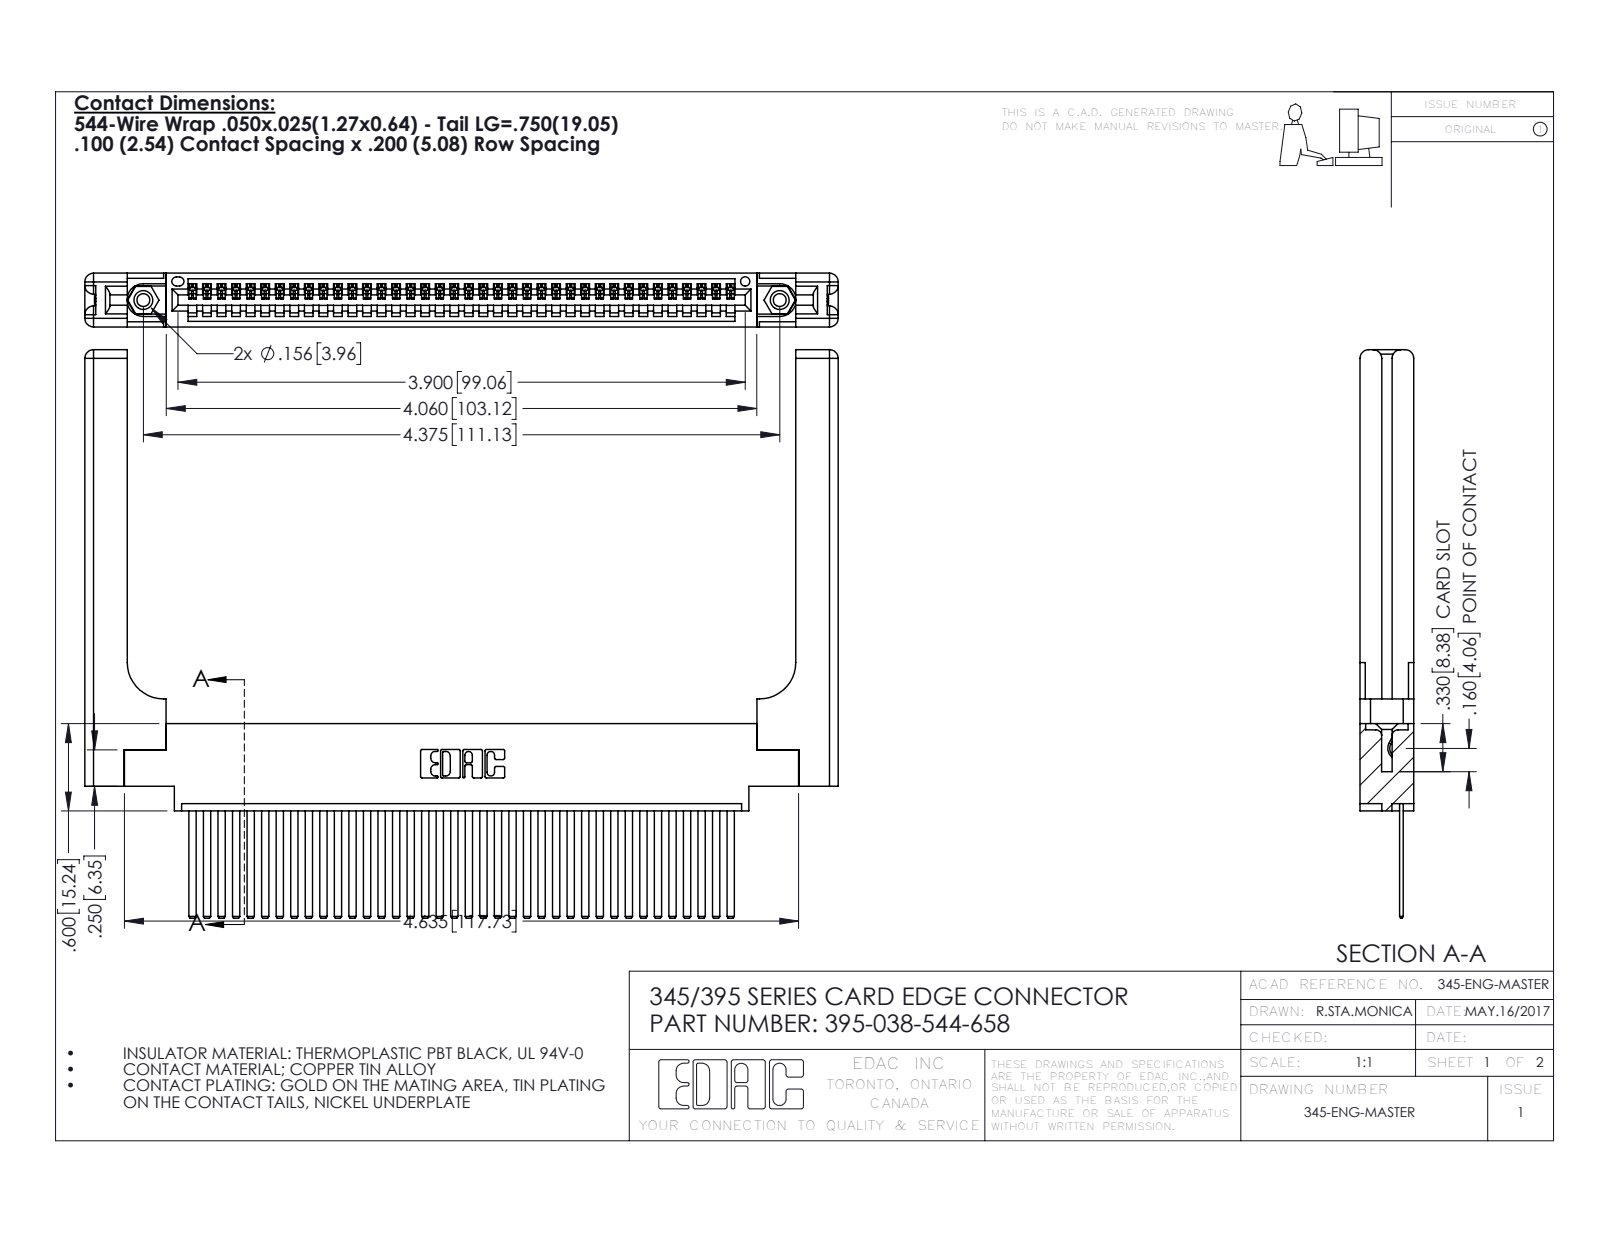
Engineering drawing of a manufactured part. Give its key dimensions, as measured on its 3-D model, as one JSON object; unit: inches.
{"part_name": "345 Part_0.170 Offset - 0.156 Dia-TH; 345-220-058_345-220-058; 395-038-544-658; 345-250-001_345-250-001-102 (+1 more)", "step_written_by": "SolidWorks 2016 (CONFIG_CONTROL_DESIGN)", "units": "inches", "bodies": {"solids": 43, "faces": 2362, "planar": 1600, "cylindrical": 702, "other": 60}, "overall_size": [5.179, 3.907, 0.37], "volume_in3": 1.299, "surface_area_in2": 36.73, "round_holes": [[0.089, 2], [0.125, 2], [0.156, 2], [0.064, 1]], "round_bosses_or_shafts": [[0.155, 2]], "partial_cylinders_radius": [[0.006, 76], [0.01, 22], [0.06, 16], [0.007, 6], [0.031, 6], [0.026, 3], [0.03, 2], [0.031, 2]], "face_to_face_distances": [0.072, 0.298, 0.37, 0.098, 0.272, 0.025, 0.2, 0.148, 0.15, 0.225], "hole_center_spacings": [0.27, 4.139, 4.375]}
